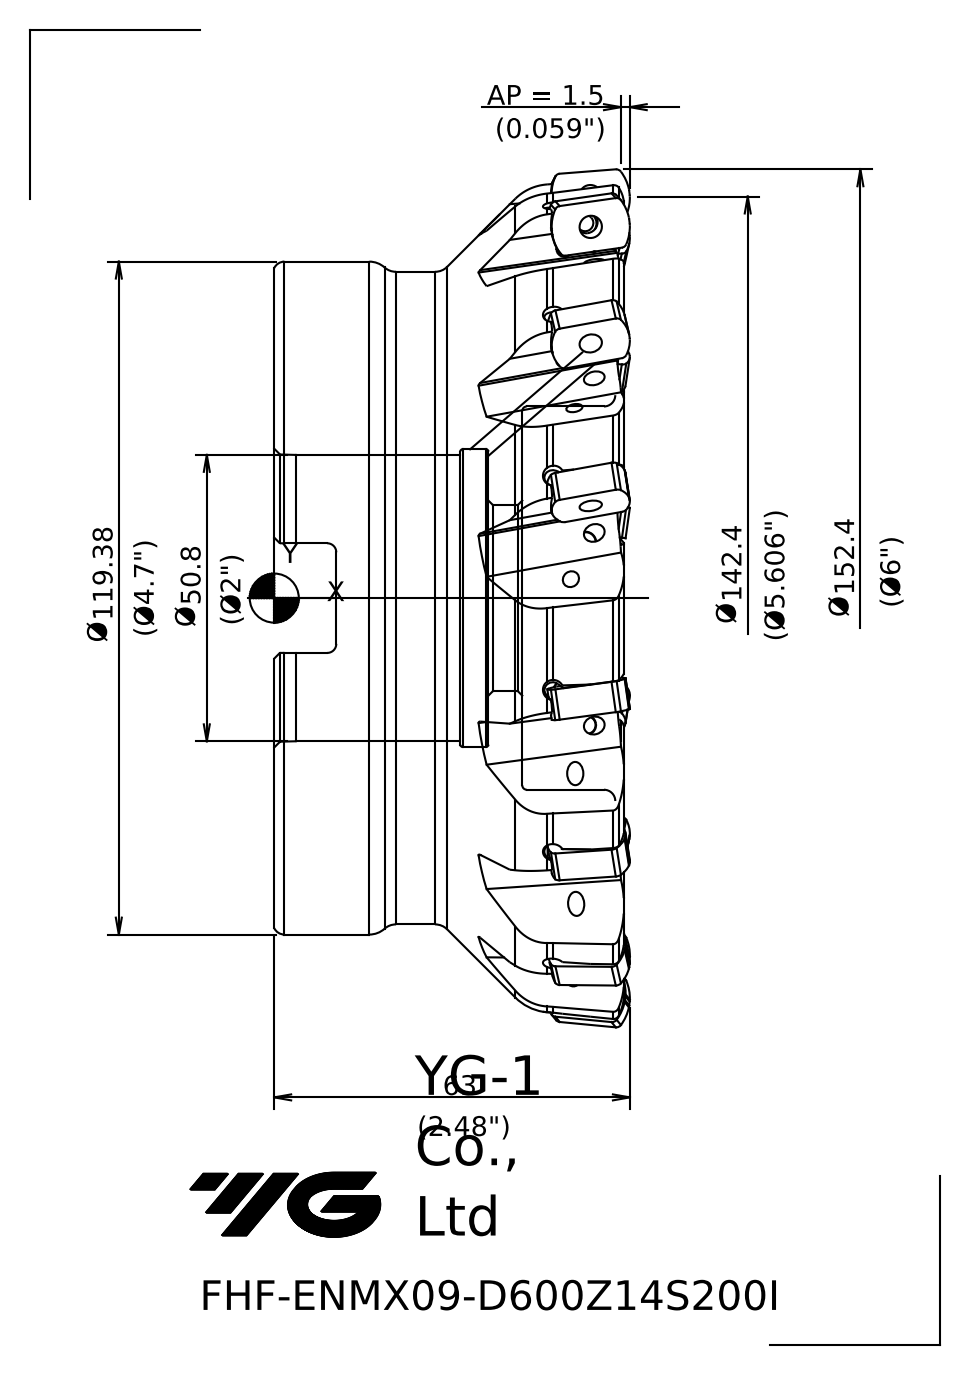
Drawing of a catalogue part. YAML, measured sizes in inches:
part_name: "subtract 6.00---2.00I; TURNING_FHF-ENMX09-D600Z14S200I"
step_written_by: "SIEMENS PLM Software NX 10.0 (CONFIG_CONTROL_DESIGN)"
units: inches
bodies: {solids: 4, faces: 477, planar: 75, cylindrical: 55, other: 347}
overall_size: [8.661, 6, 2.58]
volume: 59.6
surface_area: 181.3
round_holes:
  - {diameter: 0.157, count: 1}
  - {diameter: 1.299, count: 1}
  - {diameter: 2, count: 1}
  - {diameter: 2.079, count: 1}
  - {diameter: 2.677, count: 1}
round_bosses_or_shafts:
  - {diameter: 4.7, count: 1}
  - {diameter: 4.558, count: 1}
  - {diameter: 2.593, count: 1}
  - {diameter: 0.984, count: 1}
partial_cylinders:
  - {radius: 0.013, count: 12}
  - {radius: 0.012, count: 4}
  - {radius: 0.031, count: 4}
  - {radius: 0.039, count: 4}
  - {radius: 0.157, count: 4}
  - {radius: 0.063, count: 3}
  - {radius: 0.016, count: 2}
  - {radius: 0.315, count: 2}
face_to_face_distances: [0.686, 2.419, 1.732, 2.517, 1.831, 0.098, 0.433, 1.299, 1.985, 0.531]
